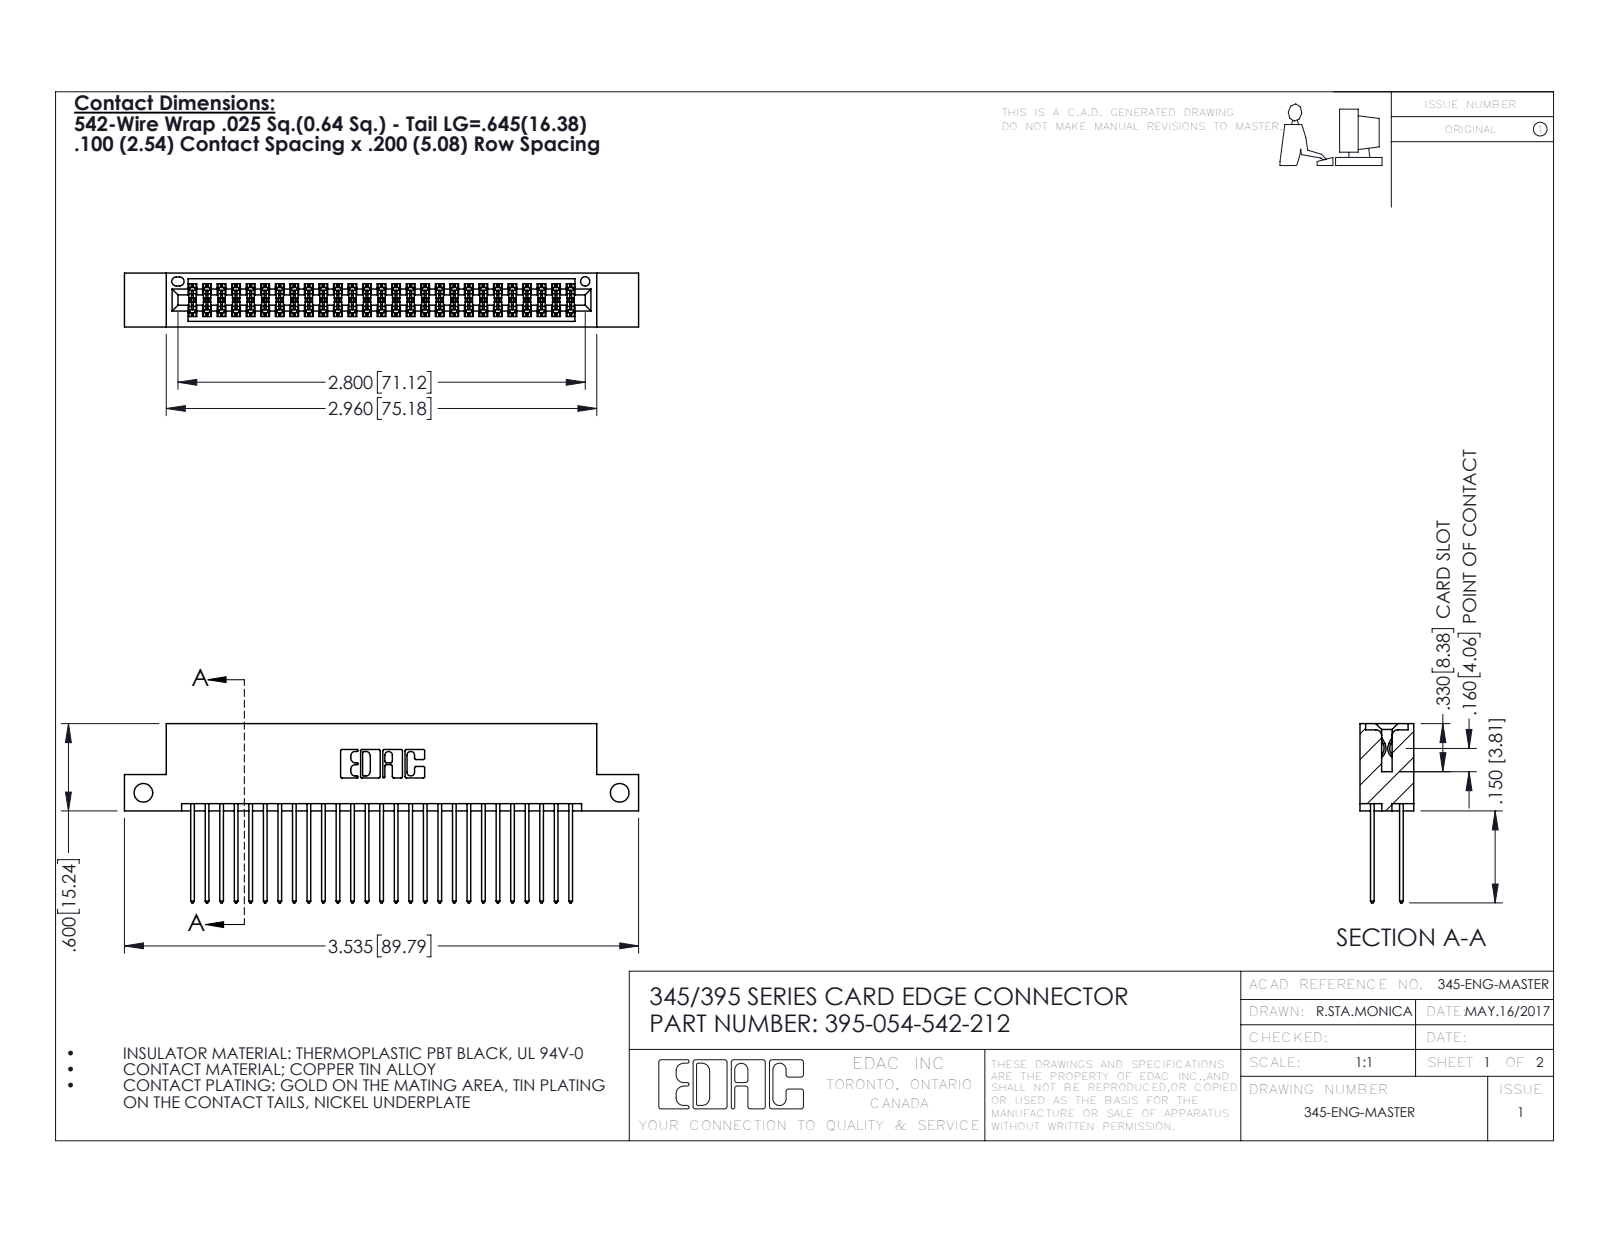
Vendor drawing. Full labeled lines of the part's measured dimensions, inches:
Part name (STEP PRODUCT): 345 Part_Flush Mounting Lugs - Side Mount; 395-054-542-212; 345-292-001_345-293-142
STEP written by: SolidWorks 2016 (CONFIG_CONTROL_DESIGN)
Units: inches
Bodies: 55 solids, 2826 faces (1862 planar, 964 cylindrical, 0 other)
Overall size (bounding box): 3.535 × 1.232 × 0.37
Volume: 0.534 in³ · Surface area: 21.2 in²
Round holes (diameter × count): ⌀0.128 ×2, ⌀0.064 ×1
Partial cylindrical surfaces — rounded edges, fillets, slot ends (radius × count): R0.006 ×81, R0.01 ×54, R0.01 ×22, R0.007 ×6, R0.031 ×6, R0.026 ×3, R0.014 ×2, R0.019 ×2
Main face-to-face distances: 0.298, 0.072, 0.2, 0.098, 0.272, 0.025, 0.37, 0.225, 0.175, 0.149
Hole centre spacings: 3.275
